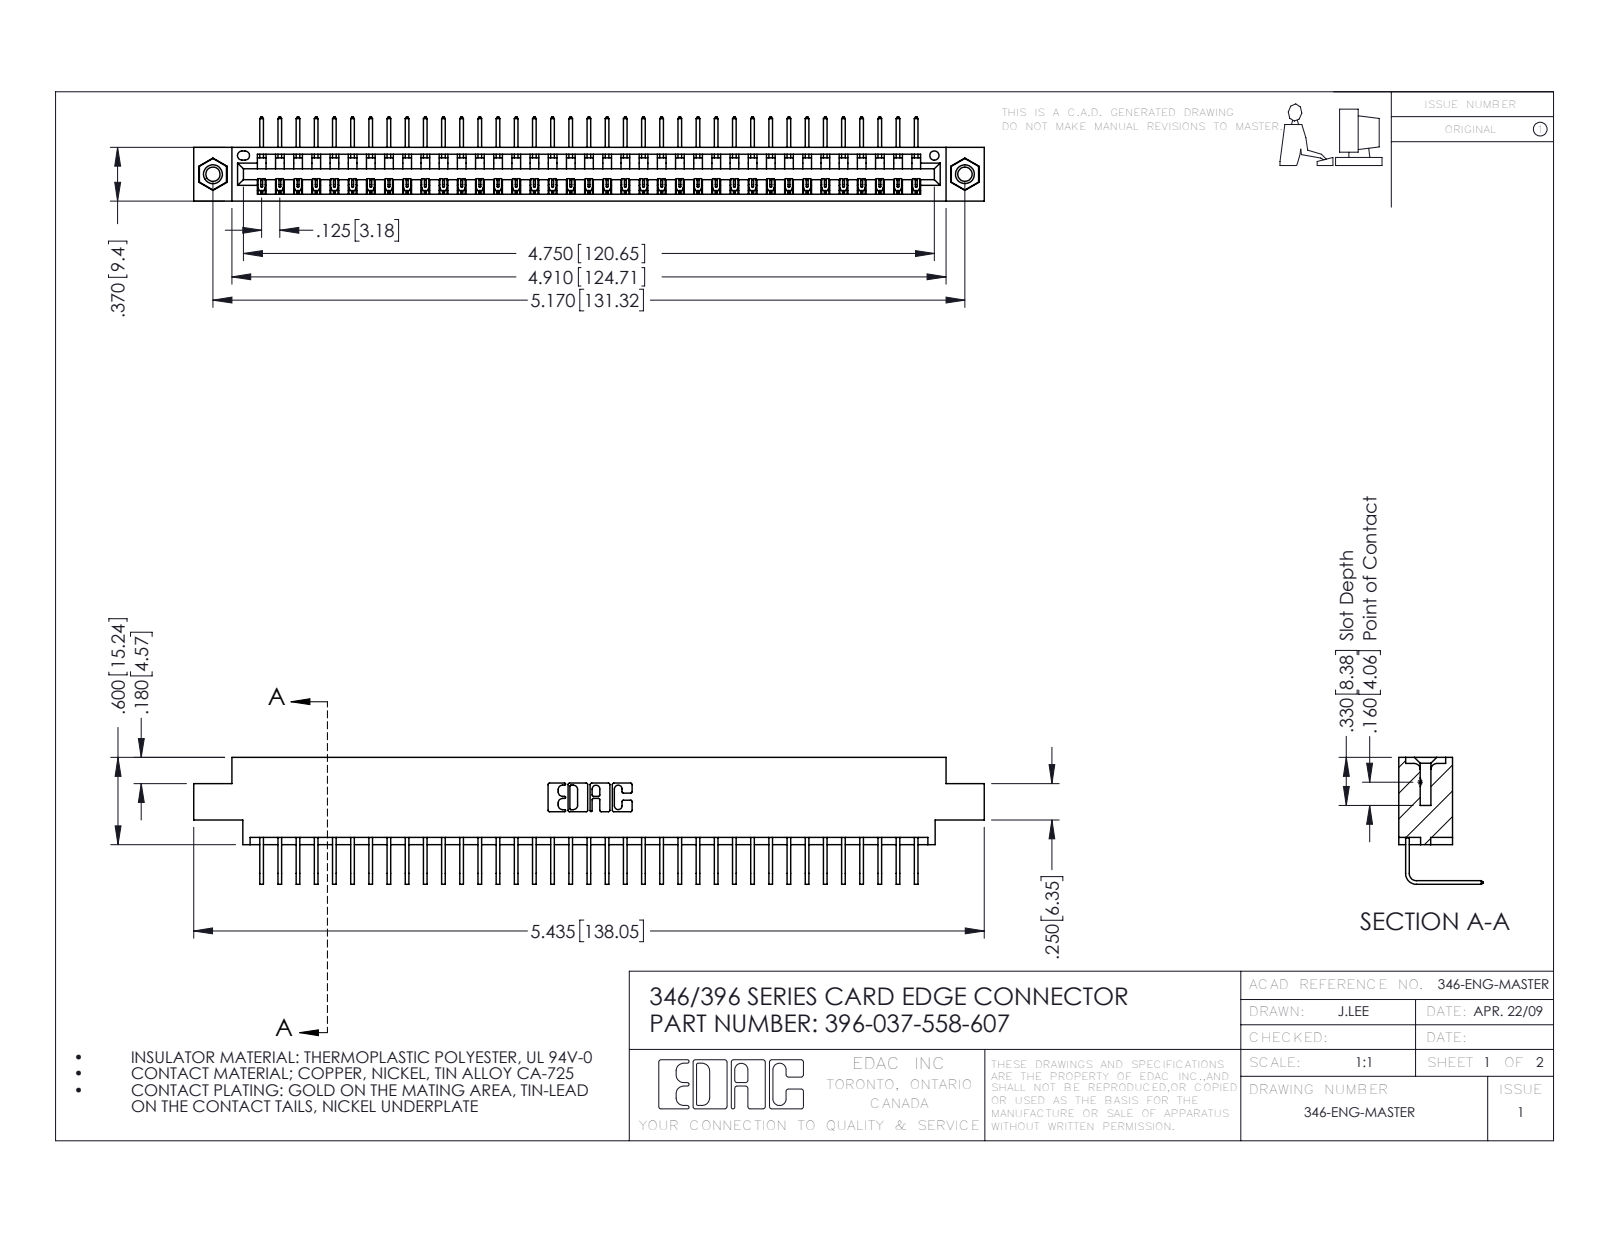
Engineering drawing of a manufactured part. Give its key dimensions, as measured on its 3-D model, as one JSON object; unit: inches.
{"part_name": "345-250-001_345-250-005-103; 396-037-558-607; 346 Part_0.170 Offset - 0.156 Dia-TI; 345-292-001_558 Tail - 2", "step_written_by": "SolidWorks 2016 (CONFIG_CONTROL_DESIGN)", "units": "inches", "bodies": {"solids": 40, "faces": 2406, "planar": 1666, "cylindrical": 724, "other": 16}, "overall_size": [5.435, 0.873, 0.58], "volume_in3": 0.802, "surface_area_in2": 26.81, "round_holes": [[0.098, 2], [0.125, 2], [0.156, 2], [0.064, 1]], "round_bosses_or_shafts": [[0.155, 2]], "partial_cylinders_radius": [[0.006, 74], [0.01, 22], [0.007, 6], [0.031, 6], [0.026, 3], [0.031, 2], [0.04, 2], [0.014, 1]], "face_to_face_distances": [0.322, 0.048, 0.37, 0.25, 0.298, 0.025, 0.072, 0.222, 0.148, 0.1], "hole_center_spacings": [0.246, 4.961, 5.17]}
